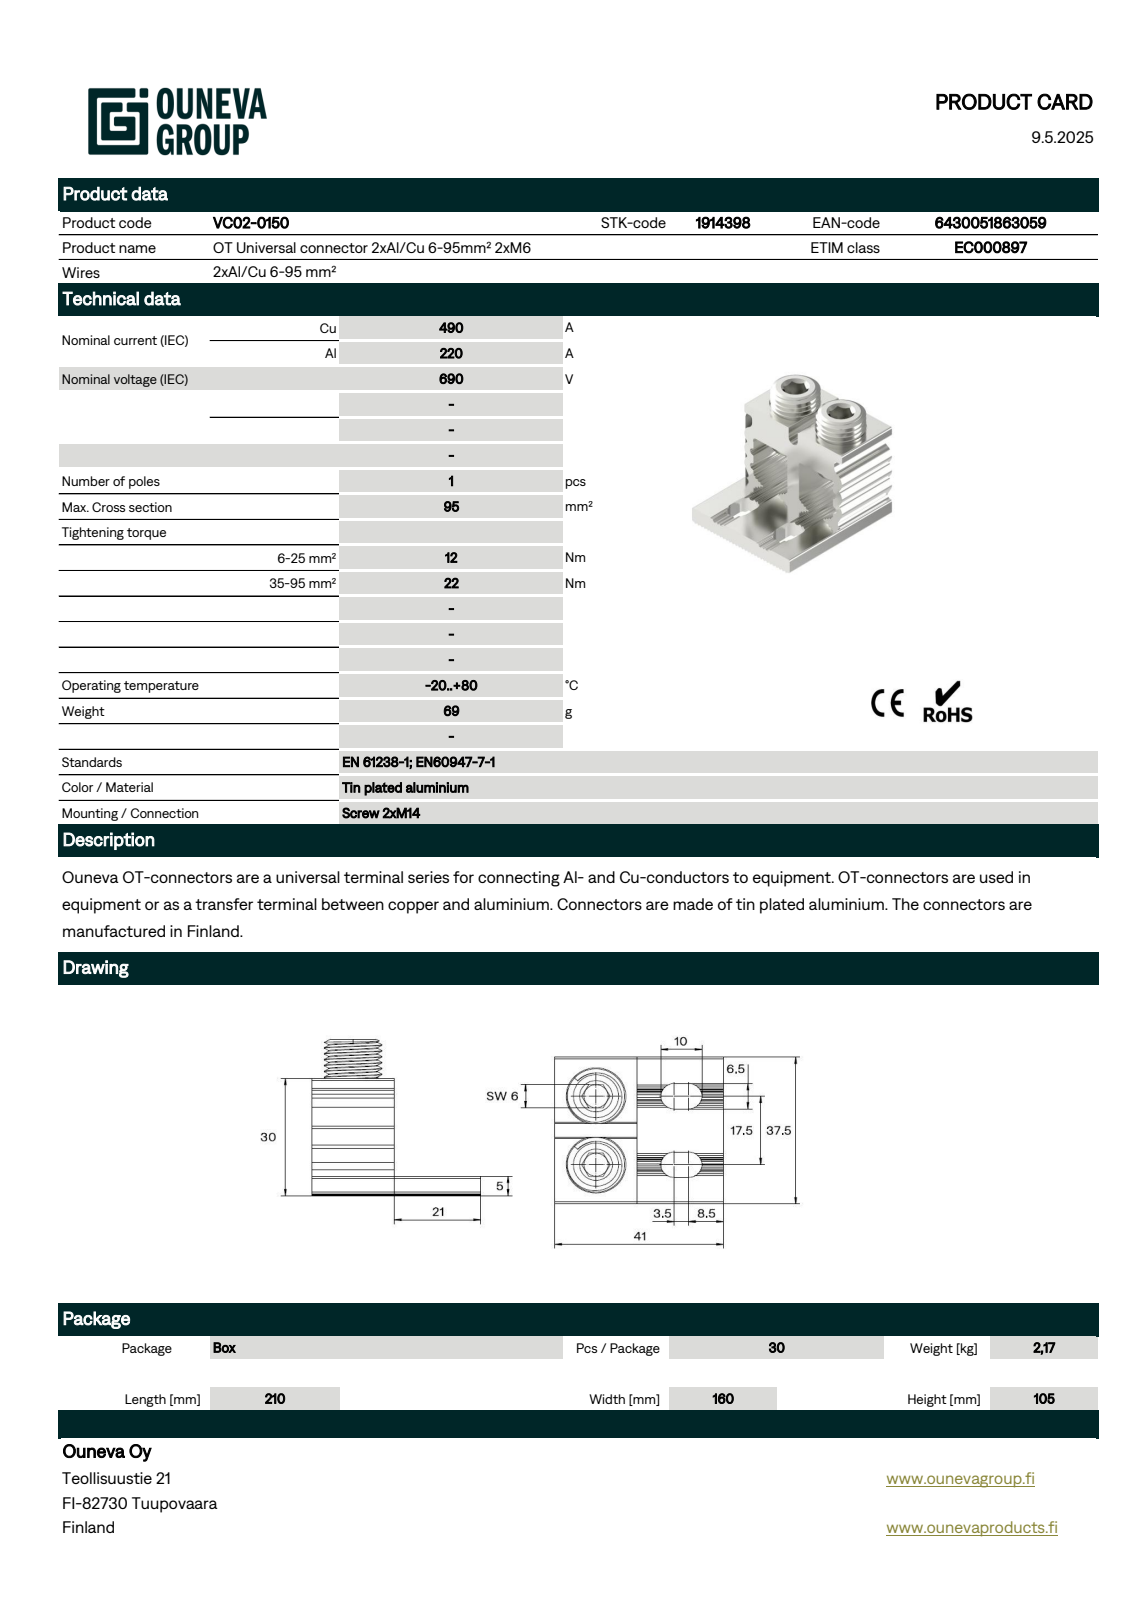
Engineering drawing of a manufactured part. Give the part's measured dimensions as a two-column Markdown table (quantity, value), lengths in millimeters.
| quantity | value |
| --- | --- |
| part name | VC02-0150_OT_2x95_2xM6 |
| STEP written by | Creo Elements/Direct Modeling 20.6A 14-Oct-2023 (C) Parametric Technology GmbH (AUTOMOTIVE_DESIGN) |
| units | millimeters |
| bodies | 1 solid, 376 faces (152 planar, 212 cylindrical, 12 other) |
| overall size | 41 × 39.72 × 37.5 |
| volume | 19 058 mm³ |
| surface area | 10 164 mm² |
| round bosses / shafts (diameter × count) | 14 × 2 |
| partial cylindrical surfaces (radius × count) | 0.3 × 111, 0.5 × 14, 0.5 × 8, 1 × 6, 3 × 6, 1.05 × 4, 3.25 × 4, 0.4 × 3 |
| main face-to-face distances | 21, 20, 25, 16.5, 3.5, 17.5, 10, 0.96, 13, 17 |
